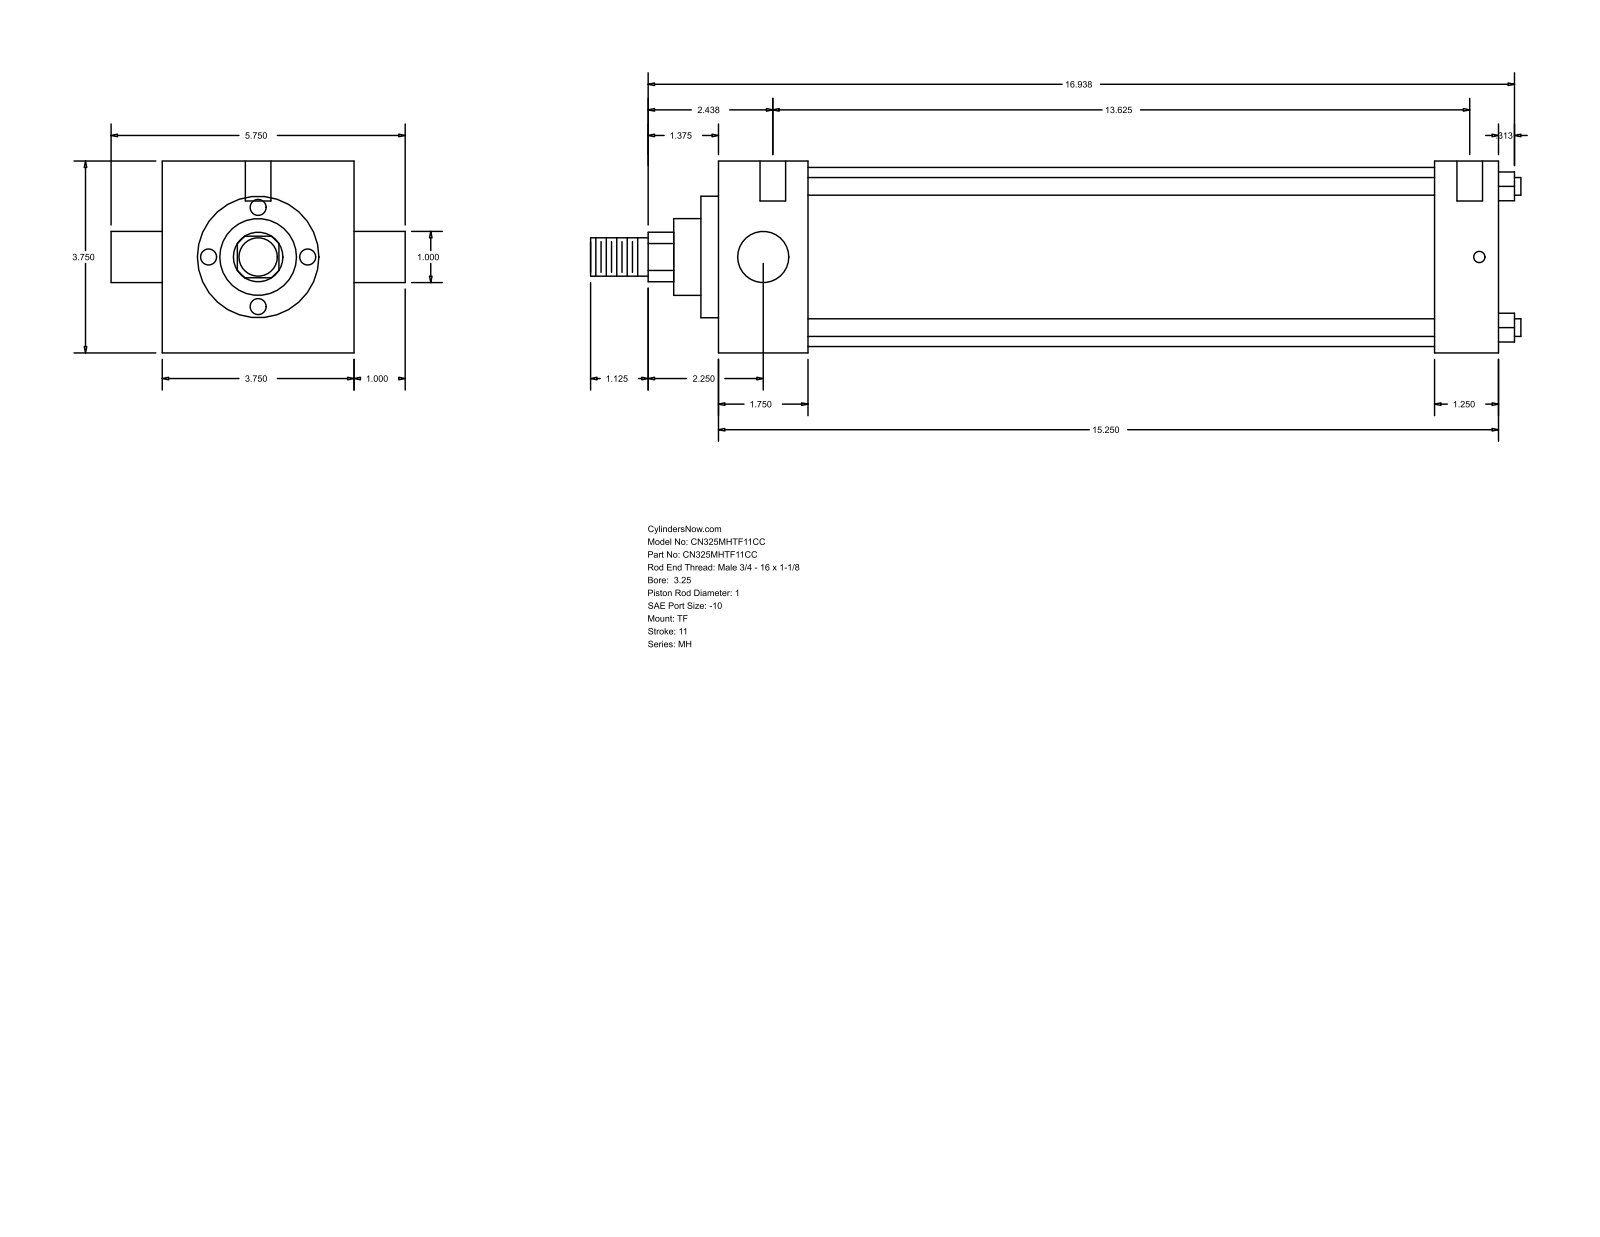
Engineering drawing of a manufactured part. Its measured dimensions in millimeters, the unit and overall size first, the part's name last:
Units: millimetres
Overall size (bounding box): 461.96 × 146.05 × 95.25
Round holes (diameter × count): ⌀5.56 ×3, ⌀12.7 ×2
Round bosses / shafts (diameter × count): ⌀8.76 ×4, ⌀25.4 ×2, ⌀88.9 ×1, ⌀60.33 ×1, ⌀38.1 ×1, ⌀19.05 ×1
Partial cylindrical surfaces — rounded edges, fillets, slot ends (radius × count): R12.29 ×1
Main face-to-face distances: 95.24, 387.35, 44.46, 355.6, 311.14, 342.89, 31.75, 8.73, 53.19, 364.33
Hole centre spacings: 1.58, 4.76, 346.08, 347.66, 350.84, 352.42
Bodies: 0 solids, 86 faces (61 planar, 25 cylindrical, 0 other)
Part name (STEP PRODUCT): MH_TF__0325_1
STEP written by: GSSL Pune (CONFIG_CONTROL_DESIGN)
